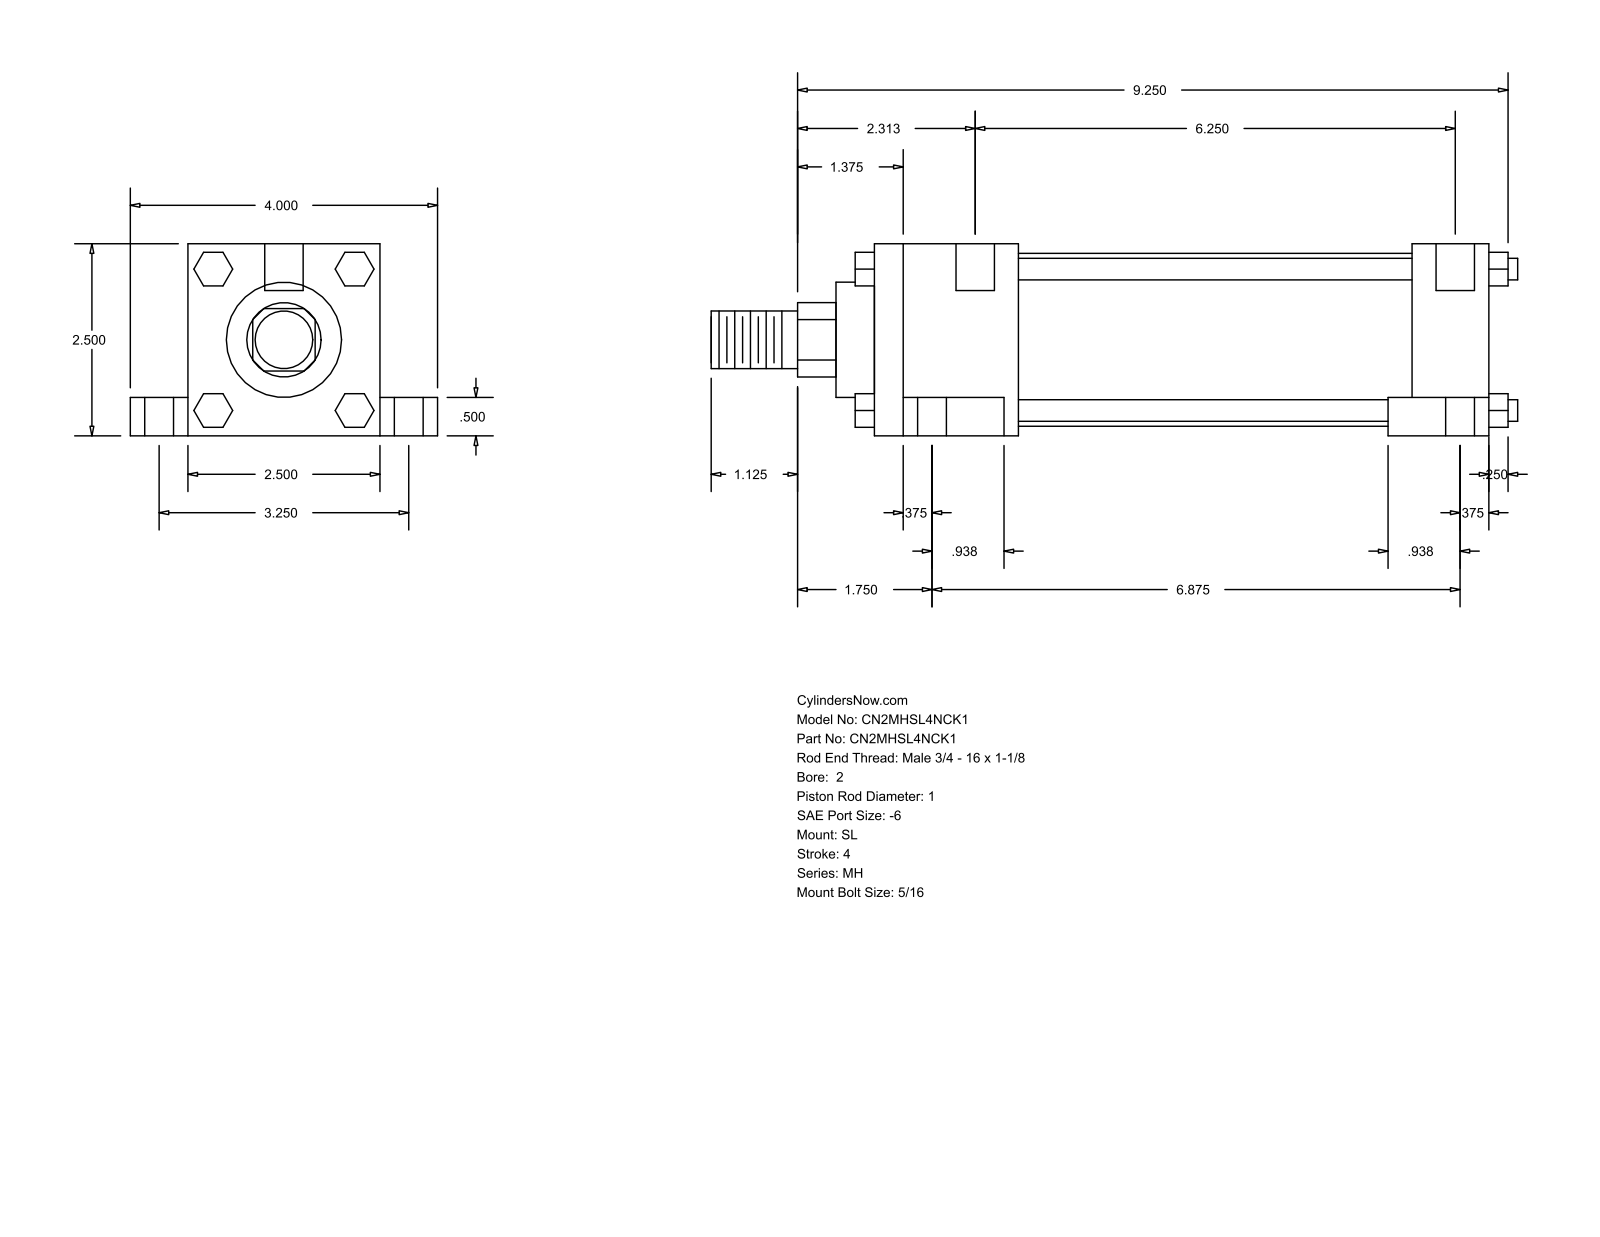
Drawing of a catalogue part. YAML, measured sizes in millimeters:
part_name: "MH_SL__0200_1"
step_written_by: "GSSL Pune (CONFIG_CONTROL_DESIGN)"
units: millimeters
bodies: {solids: 0, faces: 148, planar: 112, cylindrical: 36, other: 0}
overall_size: [266.7, 101.6, 63.5]
round_holes:
  - {diameter: 5.56, count: 4}
  - {diameter: 9.53, count: 4}
  - {diameter: 15.88, count: 4}
  - {diameter: 12.7, count: 2}
round_bosses_or_shafts:
  - {diameter: 7.14, count: 4}
  - {diameter: 57.15, count: 1}
  - {diameter: 38.1, count: 1}
  - {diameter: 25.4, count: 1}
  - {diameter: 19.05, count: 1}
partial_cylinders:
  - {radius: 12.29, count: 1}
face_to_face_distances: [63.5, 203.2, 12.7, 19.05, 50.8, 82.55, 25.4, 177.8, 47.63, 130.17]
hole_center_spacings: [41.3, 42.36, 43.67, 82.54, 165.56, 166.68, 170.17, 174.62]
